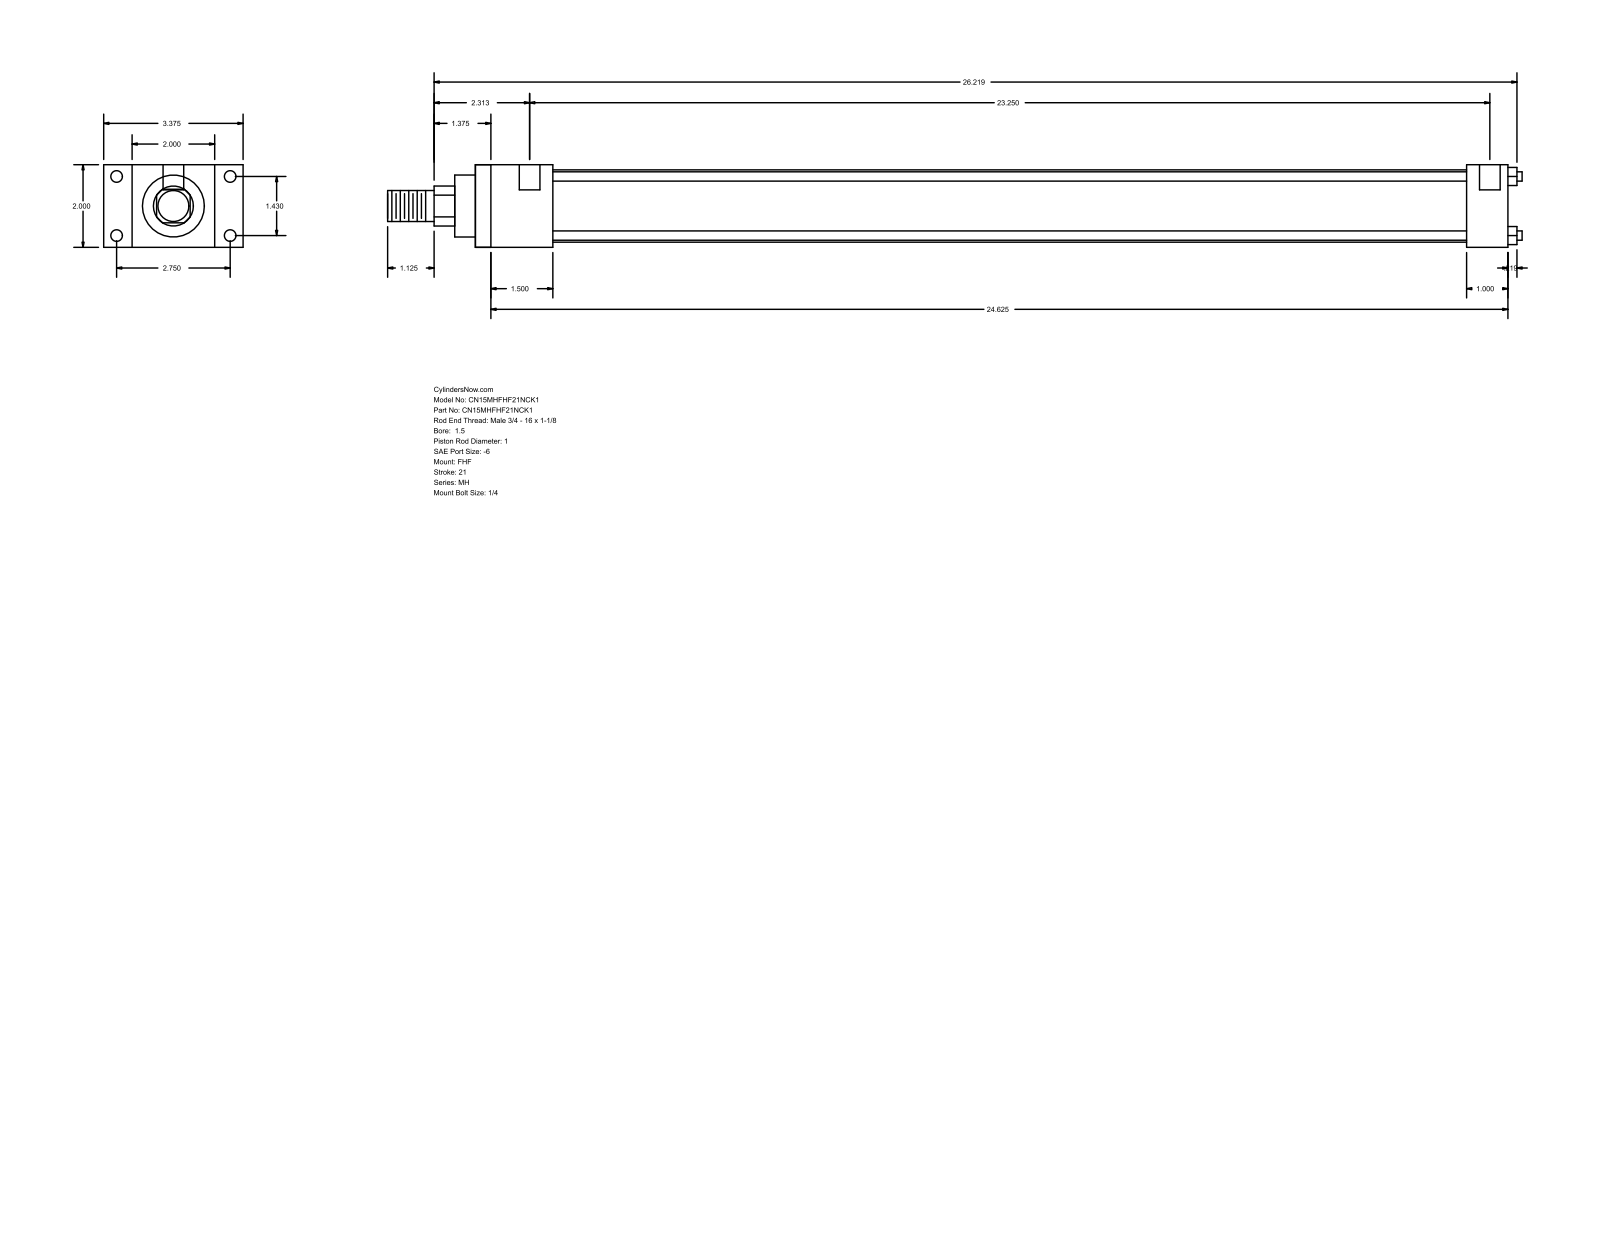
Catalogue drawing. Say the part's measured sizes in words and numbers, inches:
The part is named "MH_FHF__0150_1". Its 3-D file was written by "GSSL Pune (CONFIG_CONTROL_DESIGN)". It is 0 solids with 88 faces: 60 planar, 28 cylindrical and 0 other. Overall it measures 27.469 by 3.375 by 2 inches. Round holes: 4 of diameter 0.219, 4 of diameter 0.281, 2 of diameter 0.5. Round bosses or shafts: 4 of diameter 0.225, 1 of diameter 1.75, 1 of diameter 1.5, 1 of diameter 1, 1 of diameter 0.75. Partial cylindrical surfaces (rounded edges, fillets, slot ends): 1 of radius 0.484. The main face-to-face distances are 2, 0.687, 2.687, 1.875, 3.375, 25, 23.125, 1, 24, 22.125. The hole center spacings are 1.43, 2.75, 3.099, 23.375, 0.125, 23.25.
